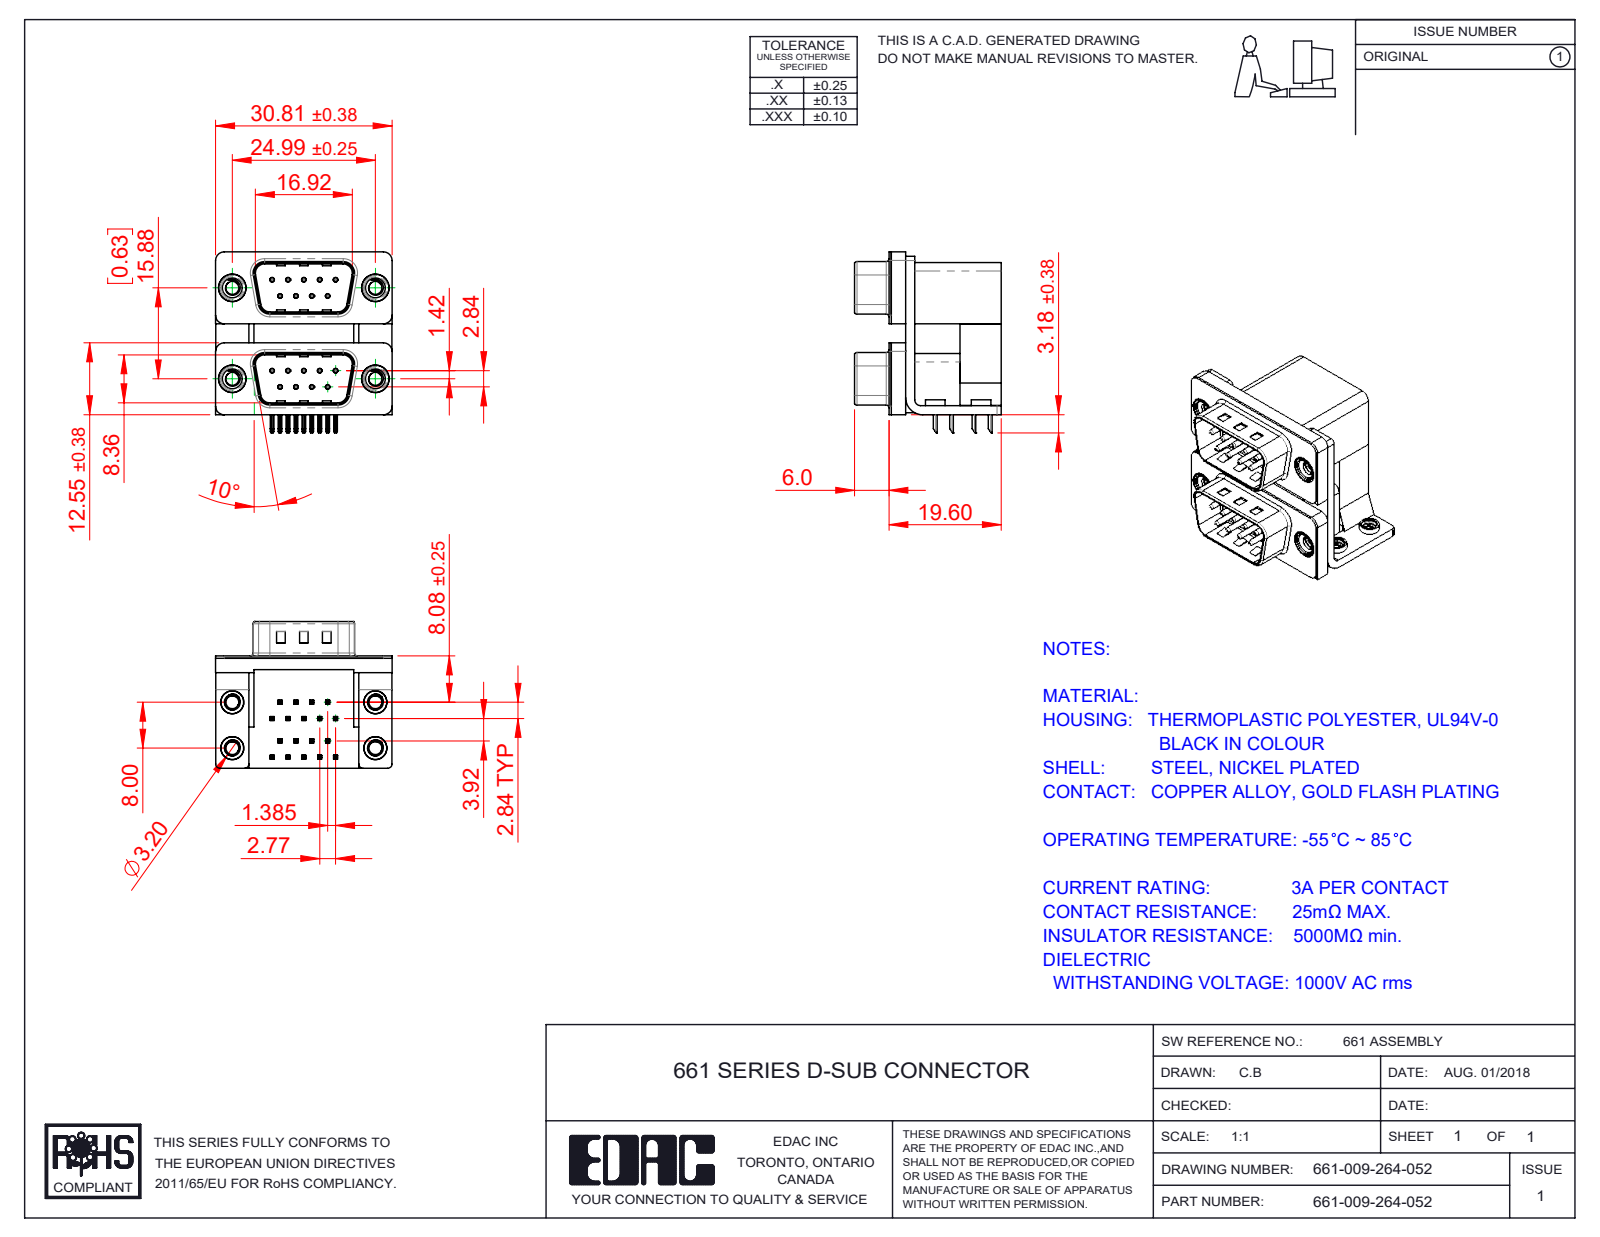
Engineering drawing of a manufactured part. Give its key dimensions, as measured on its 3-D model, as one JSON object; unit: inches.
{"part_name": "661 Housing Spacer_09 Contacts L; 661-009-264-052; 661 Housing Upper_09 Contacts L; 661 Shell_09 Contacts (+8 more)", "step_written_by": "SolidWorks 2020 (CONFIG_CONTROL_DESIGN)", "units": "inches", "bodies": {"solids": 33, "faces": 2088, "planar": 1164, "cylindrical": 670, "other": 254}, "overall_size": [1.244, 1.213, 1.008], "volume_in3": 0.602, "surface_area_in2": 18.07, "round_holes": [[0.014, 18], [0.031, 18], [0.089, 8], [0.108, 4], [0.126, 4], [0.138, 4], [0.157, 4], [0.189, 4], [0.197, 4]], "round_bosses_or_shafts": [[0.03, 18], [0.193, 4], [0.187, 4], [0.157, 4], [0.154, 4], [0.134, 4]], "partial_cylinders_radius": [[0.01, 72], [0.005, 36], [0.02, 16], [0.059, 13], [0.03, 8], [0.035, 8], [0.063, 8], [0.079, 8]], "face_to_face_distances": [0.016, 0.098, 0.657, 0.756, 0.625, 0.063, 0.283, 0.374, 0.472, 0.772], "hole_center_spacings": [0.124, 0.635, 0.109, 0.625, 0.662, 0.739, 0.218, 0.198]}
